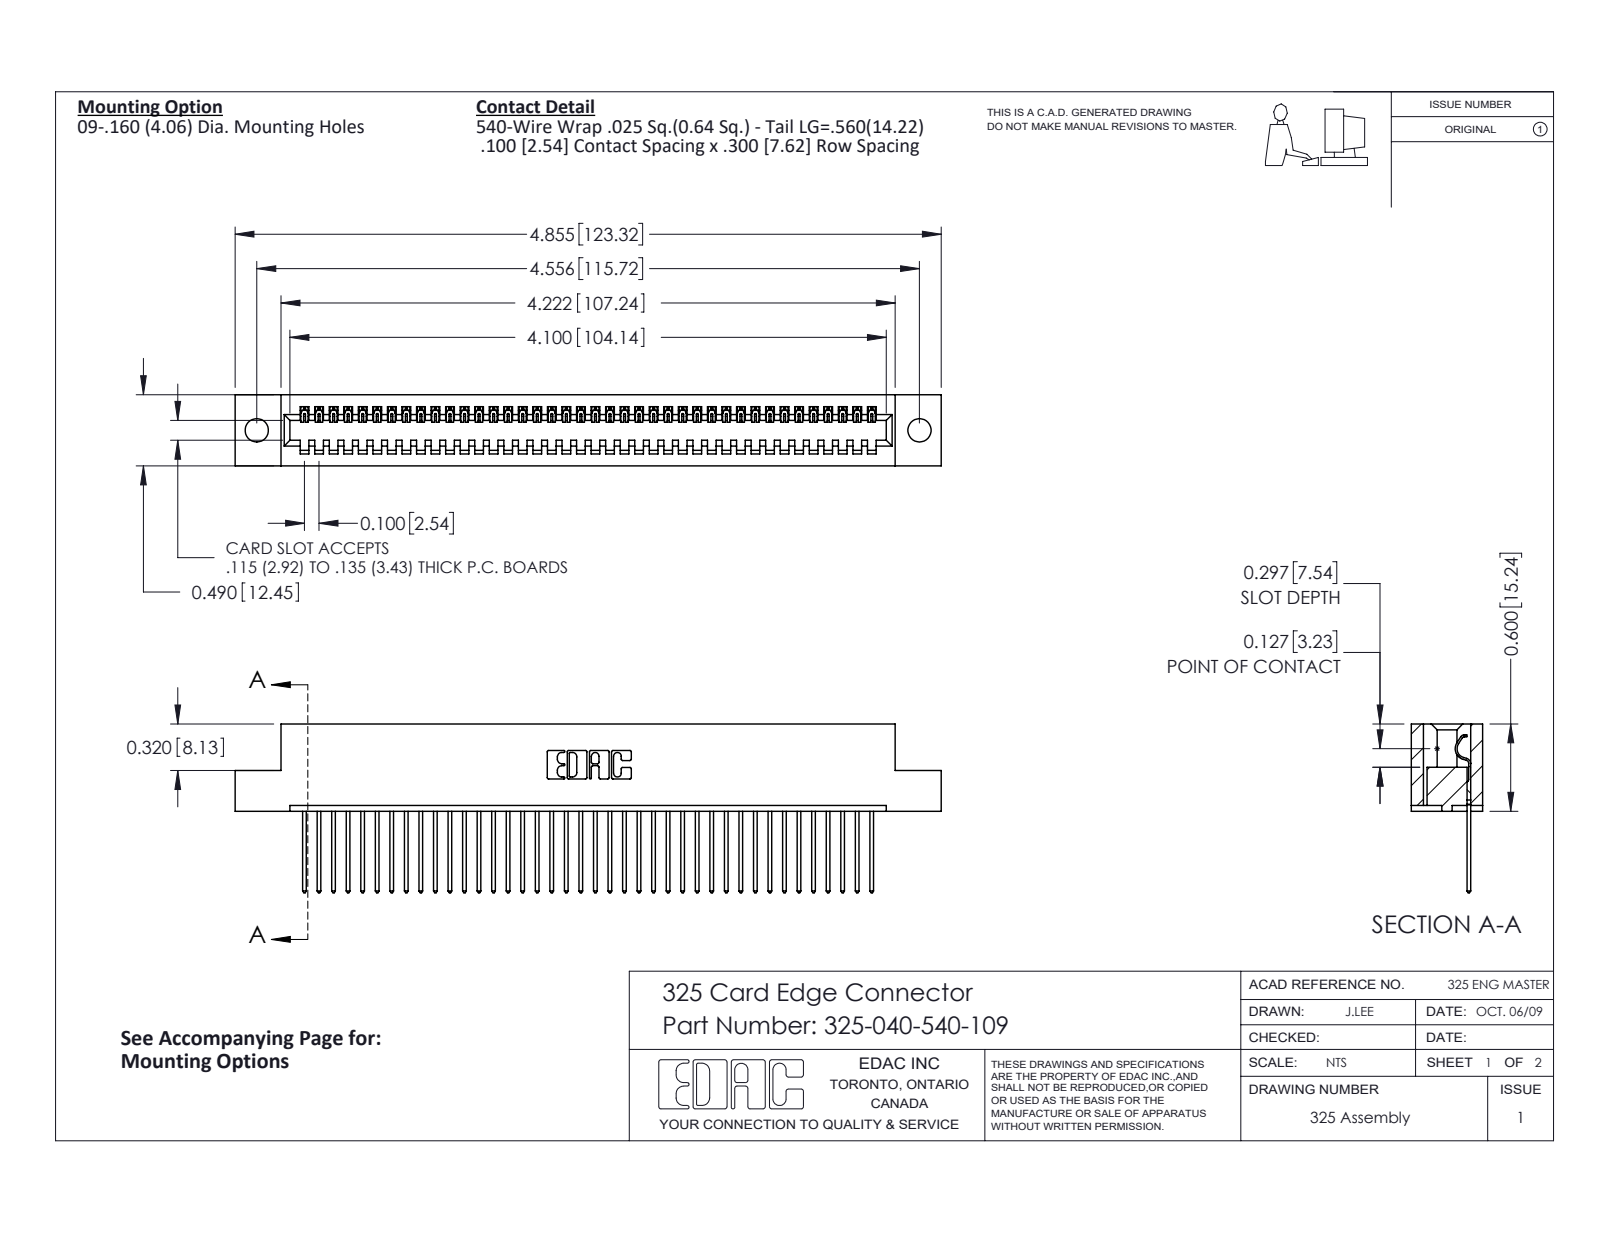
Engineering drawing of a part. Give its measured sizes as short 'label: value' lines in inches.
name: 325-040-540-109; 325-292-001_325-293-140; 325 Part_.160 TH
written by: SolidWorks 2016 (CONFIG_CONTROL_DESIGN)
unit: in
bodies: 41 solids, 2434 faces (1750 planar, 684 cylindrical, 0 other)
size: 4.855 × 1.16 × 0.49
volume: 0.944 in³; area: 26.59 in²
holes: 2× ⌀0.16
rounds: 80× R0.006, 80× R0.01, 22× R0.01, 6× R0.007, 6× R0.031, 3× R0.026, 1× R0.014, 1× R0.022
face distances: 0.083, 0.407, 0.49, 0.3, 0.107, 0.383, 0.025, 0.325, 0.56, 0.263
hole spacings: 4.556
